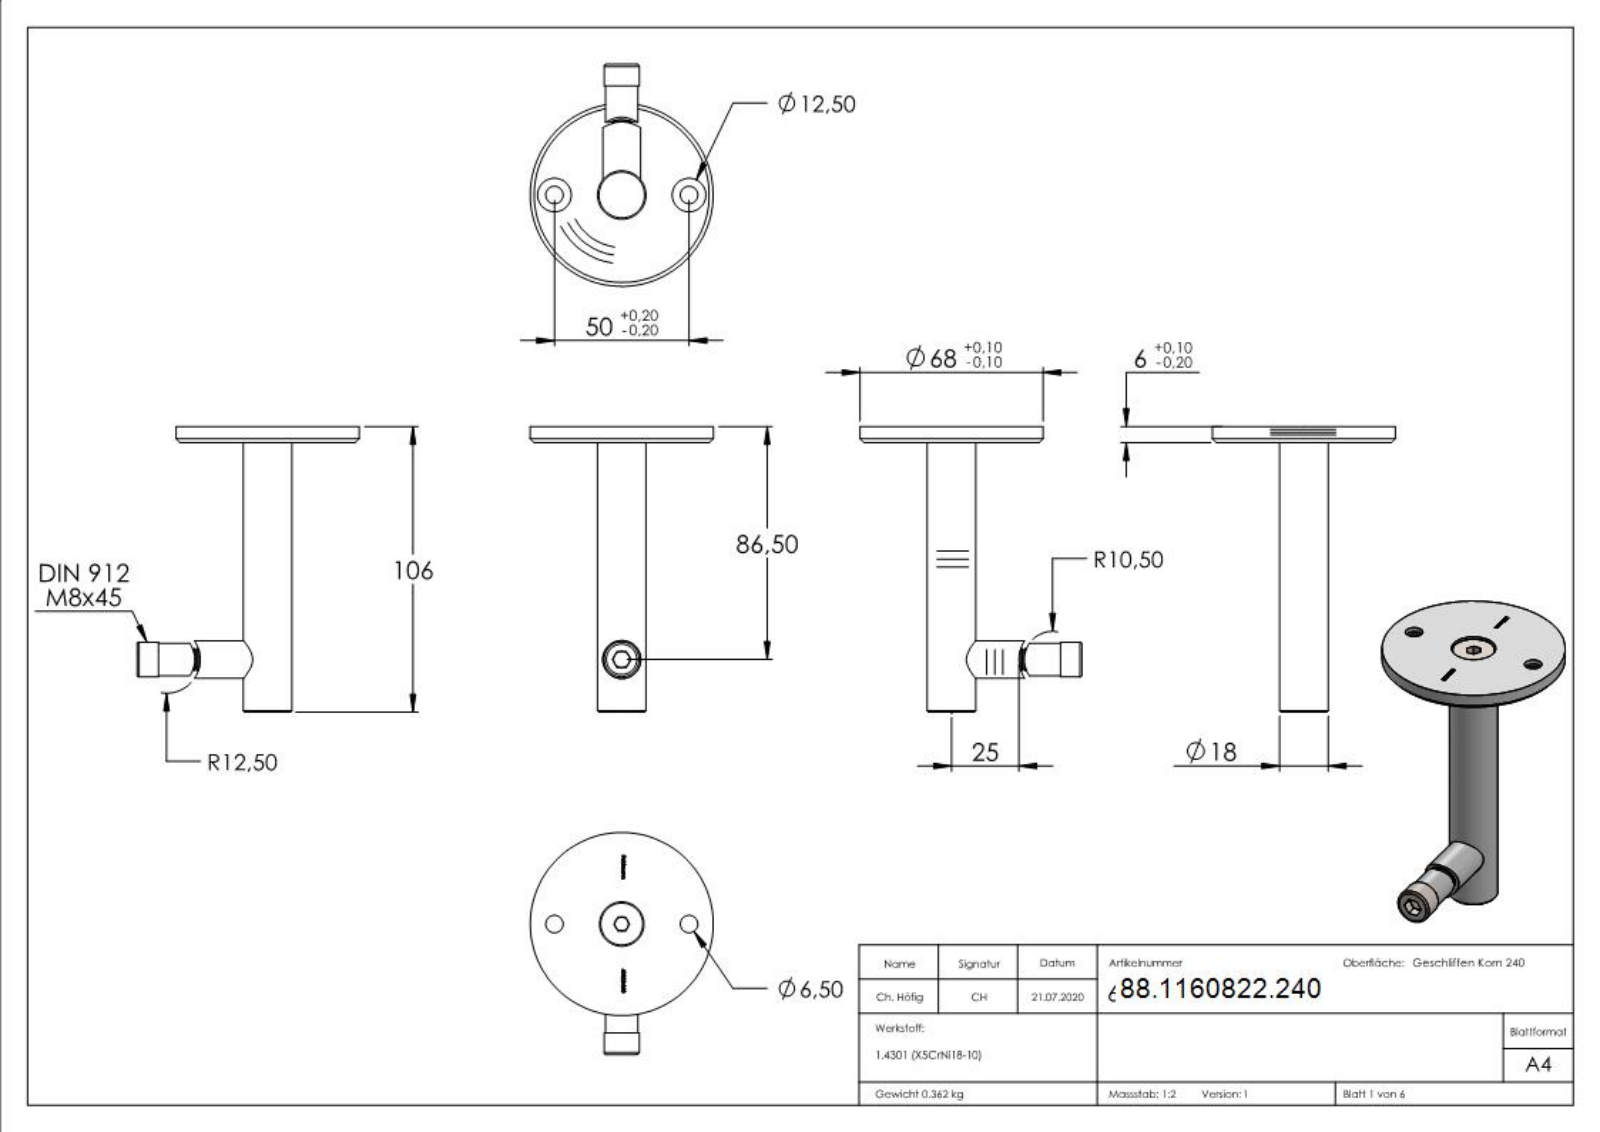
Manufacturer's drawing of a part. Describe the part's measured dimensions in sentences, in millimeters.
The part is named "60822-240; socket countersunk head screw_din_DIN 7991 - M8 x 20 --- 20S; 60822-240 Teil4_60822-240 Teil4; 60822-240 Teil3_60822-240 Teil3 (+3 more)". Its 3-D file was written by "SolidWorks 2018 (CONFIG_CONTROL_DESIGN)". It is 6 solids with 602 faces: 154 planar, 128 cylindrical and 320 other. Overall it measures 106 by 82.47 by 68 millimeters. Its volume is 49 385 cubic millimeters and its surface area 21 527 square millimeters. Round holes: 2 of diameter 6.5, 2 of diameter 6.8, 2 of diameter 12.5, 1 of diameter 8.5, 1 of diameter 9, 1 of diameter 11, 1 of diameter 14.2, 1 of diameter 16.5. Round bosses or shafts: 2 of diameter 8, 1 of diameter 68, 1 of diameter 18, 1 of diameter 15.57, 1 of diameter 14, 1 of diameter 13, 1 of diameter 12. Partial cylindrical surfaces (rounded edges, fillets, slot ends): 1 of radius 10.5, 1 of radius 12.5. The main face-to-face distances are 6, 100, 106, 105.15, 5.15, 0.85, 35.47, 43.47, 8, 6.02. The hole center spacings are 25, 50.
